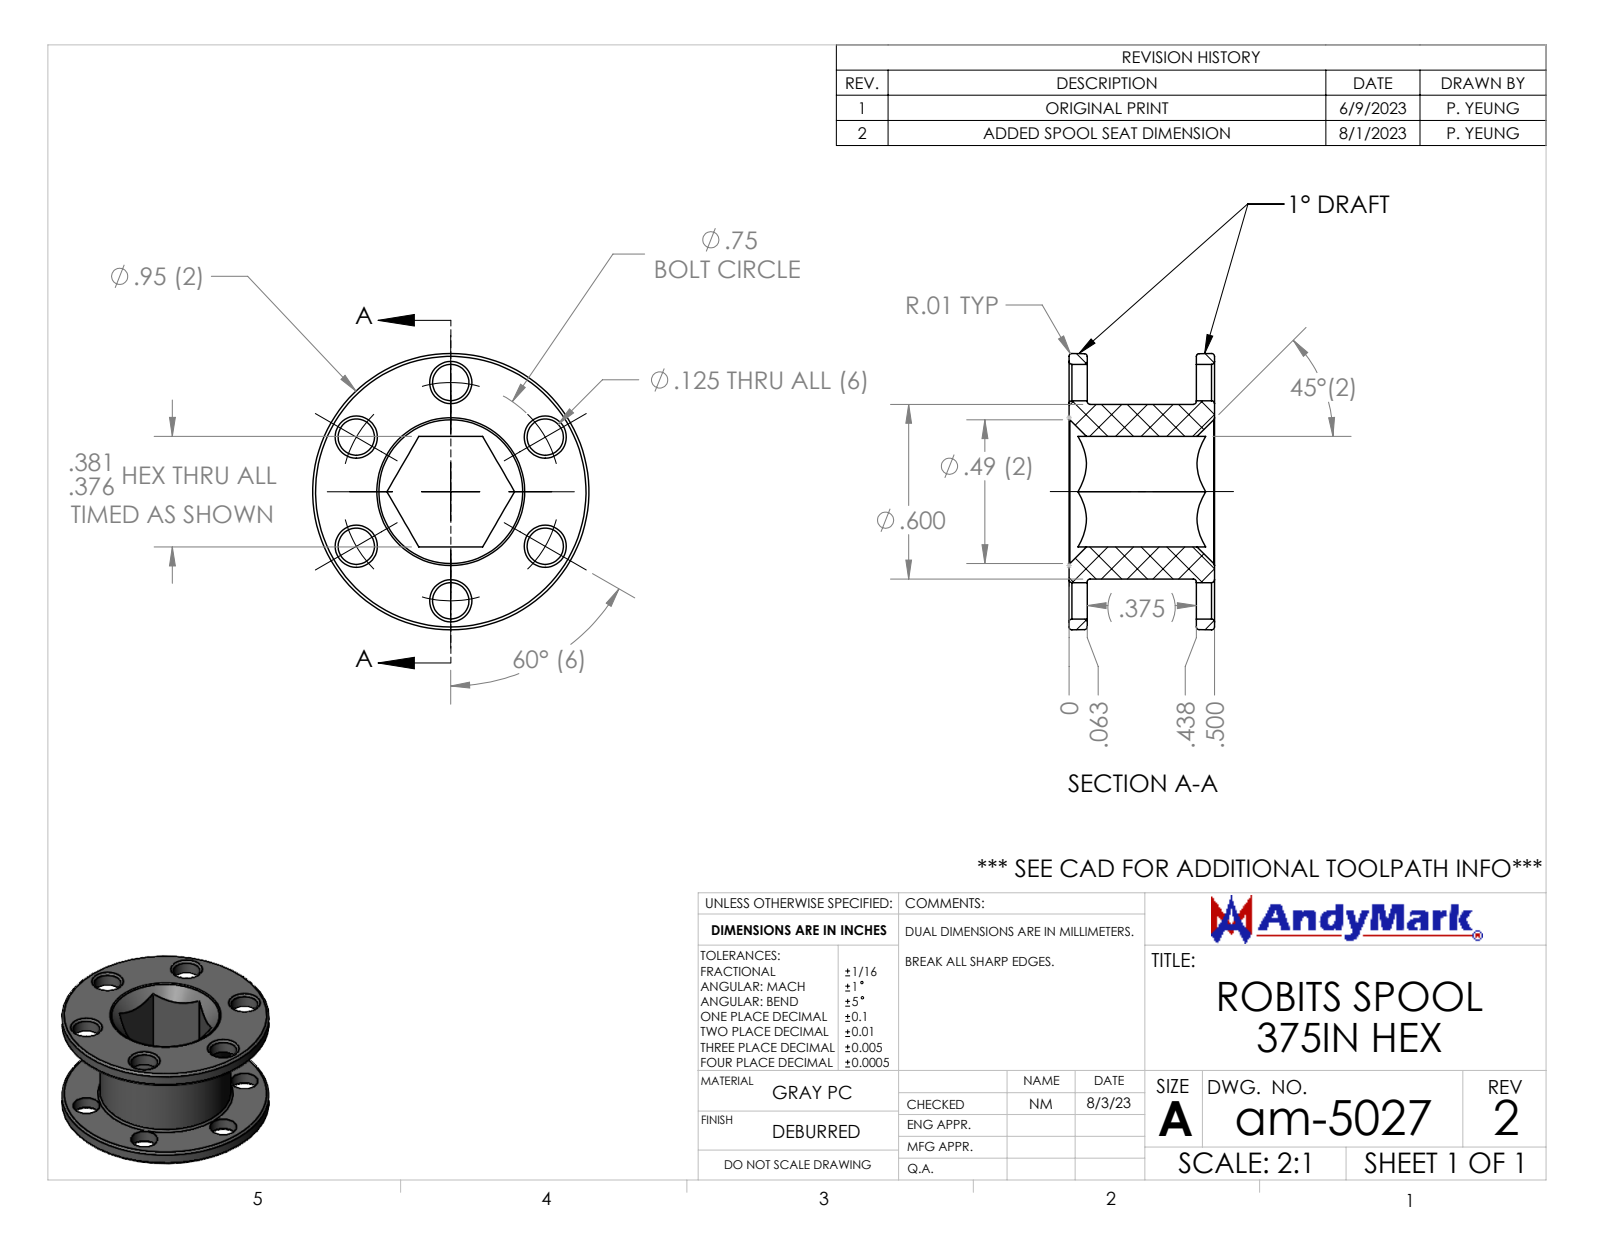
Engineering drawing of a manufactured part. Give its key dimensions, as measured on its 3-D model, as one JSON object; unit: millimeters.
{"part_name": "am-5027 Robits Spool", "step_written_by": "SolidWorks 2022 (CONFIG_CONTROL_DESIGN)", "units": "millimeters", "bodies": {"solids": 1, "faces": 84, "planar": 10, "cylindrical": 26, "other": 48}, "overall_size": [24.1, 24.1, 12.7], "volume_mm3": 1950, "surface_area_mm2": 2316, "round_holes": [[3.2, 4], [3.2, 3]], "round_bosses_or_shafts": [[15.2, 1]], "face_to_face_distances": [1.6, 11.1, 12.7, 9.5, 9.7], "hole_center_spacings": [9.5, 16.5, 9.5, 16.5, 19.1, 19.1]}
